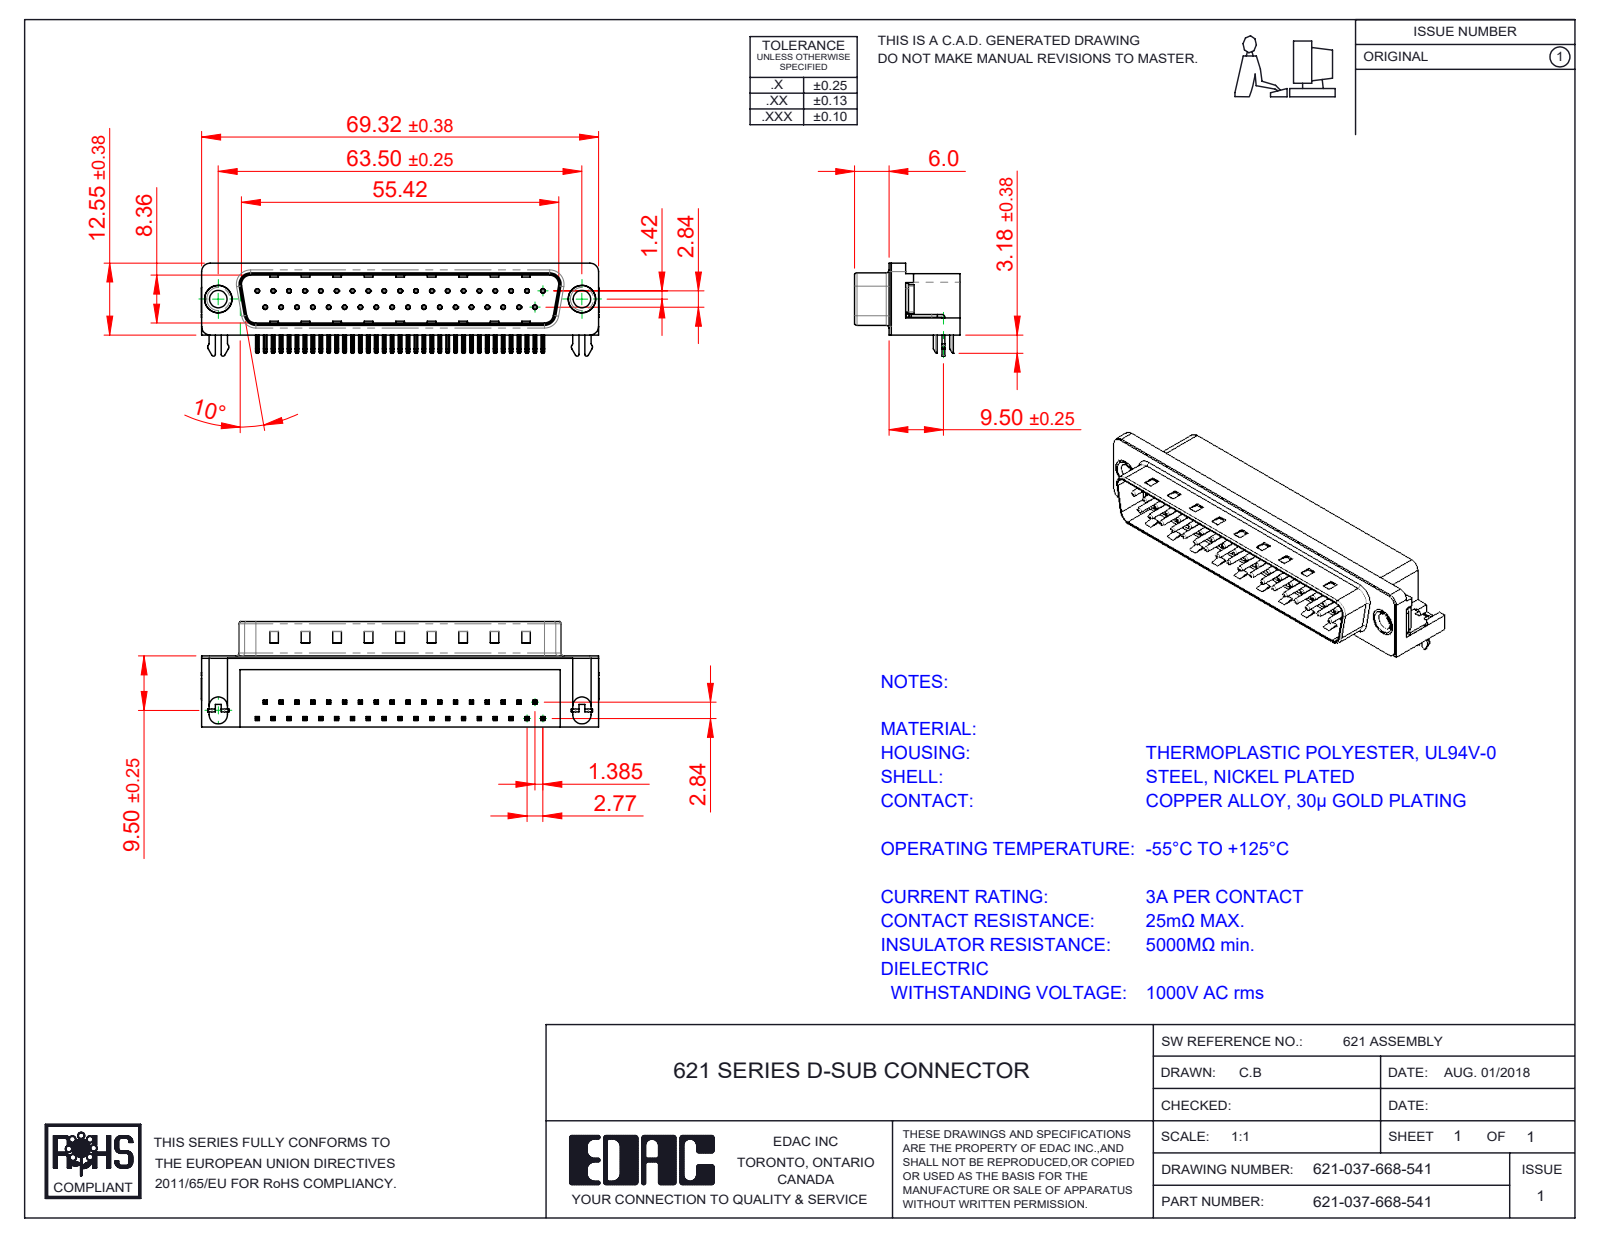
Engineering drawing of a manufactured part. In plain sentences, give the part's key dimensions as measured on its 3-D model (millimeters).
The part is named "621 Thru Hole Rivet; 621 Housing_37 Socket; 621-037-668-541; 621 4 Prong Board Lock (+3 more)". Its 3-D file was written by "SolidWorks 2016 (CONFIG_CONTROL_DESIGN)". It is 43 solids with 3279 faces: 2055 planar, 903 cylindrical and 321 other. Overall it measures 69.4 by 18.4 by 16.25 millimeters. Its volume is 8 618 cubic millimeters and its surface area 10 145 square millimeters. Round holes: 37 of diameter 0.35, 37 of diameter 0.8, 2 of diameter 2, 2 of diameter 3.05, 2 of diameter 4, 2 of diameter 4.8, 2 of diameter 5. Round bosses or shafts: 37 of diameter 0.75, 2 of diameter 4.9, 2 of diameter 4.75, 2 of diameter 3.85, 2 of diameter 3. Partial cylindrical surfaces (rounded edges, fillets, slot ends): 160 of radius 0.25, 74 of radius 0.12, 16 of radius 1, 9 of radius 0.5, 8 of radius 1.6, 7 of radius 1.5, 4 of radius 0.9, 4 of radius 2. The main face-to-face distances are 0.4, 12, 10.35, 8.76, 2.1, 1.7, 10.46, 10.86, 9, 12.4. The hole center spacings are 3.16, 2.77, 5.54, 8.31, 11.08, 13.85, 19.39, 22.16.
